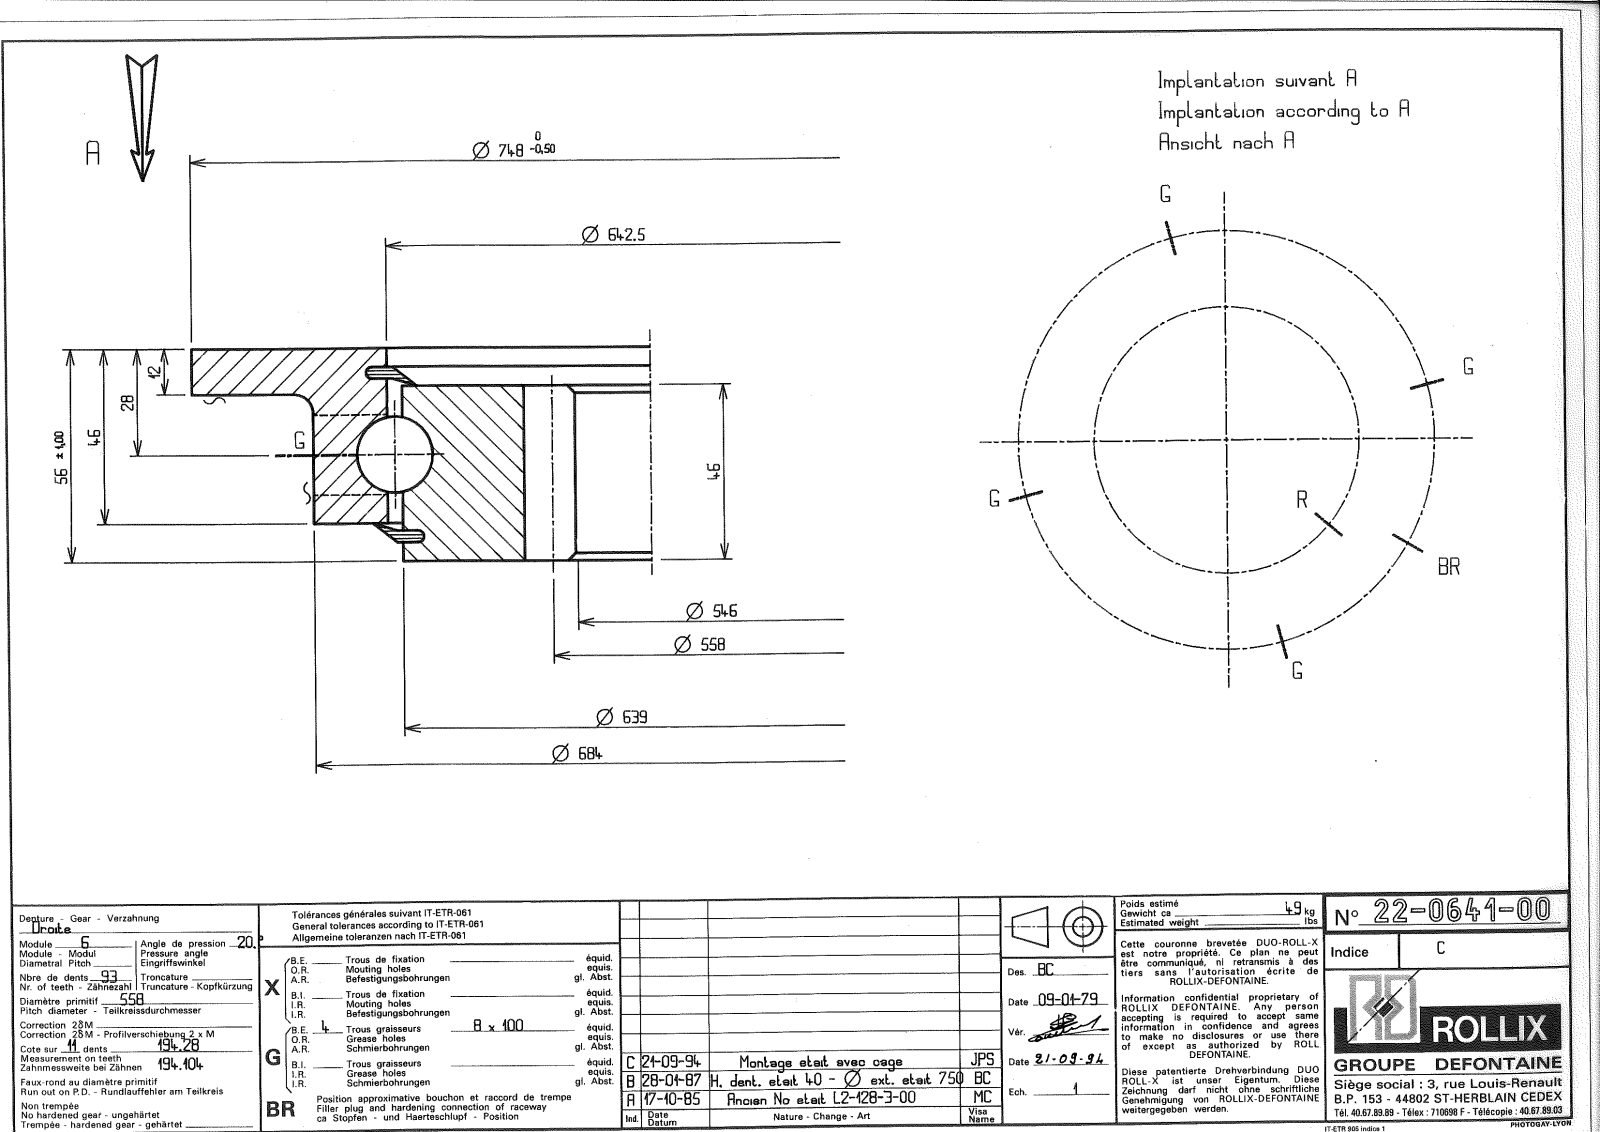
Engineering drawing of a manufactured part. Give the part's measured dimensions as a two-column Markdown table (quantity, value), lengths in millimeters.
| quantity | value |
| --- | --- |
| part name | 22-0641-00 |
| STEP written by | SolidWorks 2016 (CONFIG_CONTROL_DESIGN) |
| units | millimeters |
| bodies | 9 solids, 715 faces (239 planar, 219 cylindrical, 257 other) |
| overall size | 748 × 748 × 56 |
| volume | 5 717 000 mm³ |
| surface area | 998 560 mm² |
| round holes (diameter × count) | 7 × 4, 645.5 × 1 |
| round bosses / shafts (diameter × count) | 8 × 4, 748 × 1, 684 × 1, 636.5 × 1 |
| partial cylindrical surfaces (radius × count) | 273 × 1, 286.5 × 1 |
| main face-to-face distances | 10, 46, 56, 44, 2, 12, 34, 36, 8.05, 47.95 |
